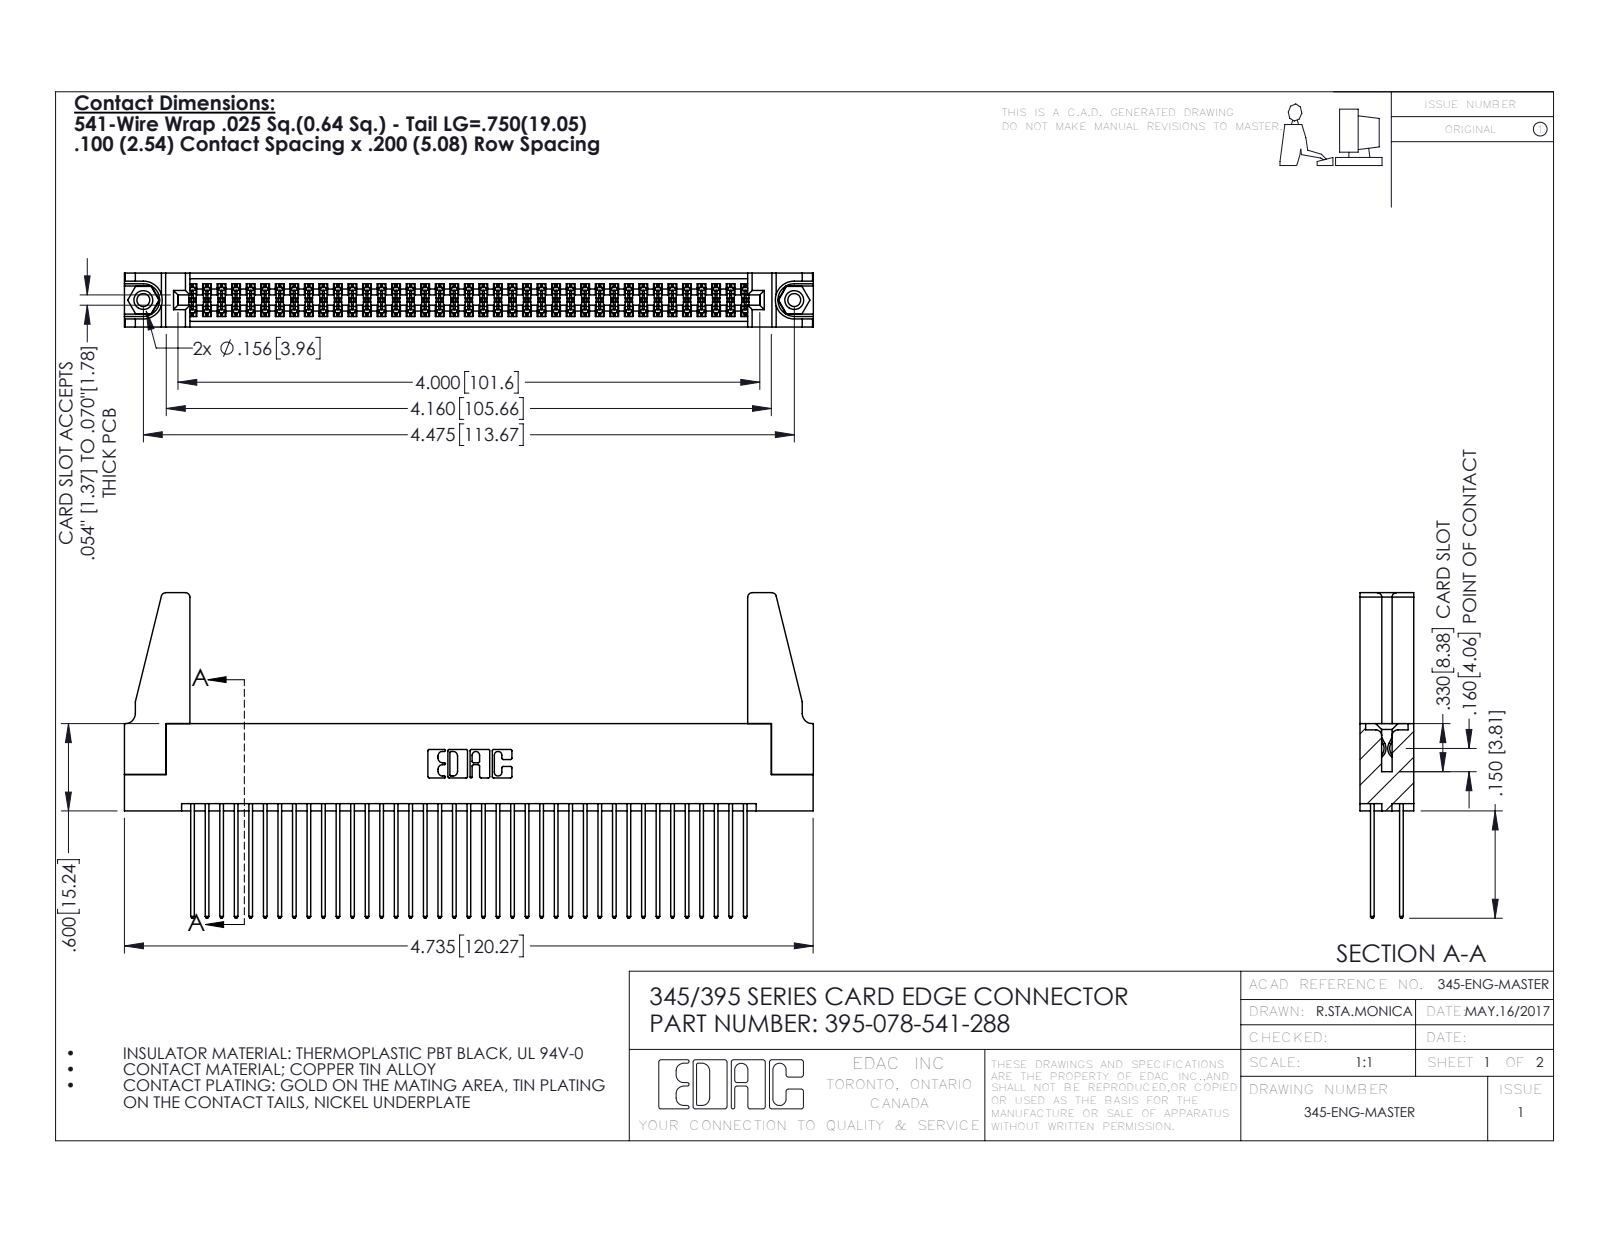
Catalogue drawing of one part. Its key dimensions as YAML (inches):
part_name: "345-220-078_345-220-088; 395-078-541-288; 345 Part_Flush Mounting Lugs - 0.156 Dia-TH; 345-250-001_345-250-001-102 (+1 more)"
step_written_by: "SolidWorks 2016 (CONFIG_CONTROL_DESIGN)"
units: inches
bodies: {solids: 83, faces: 4150, planar: 2726, cylindrical: 1408, other: 16}
overall_size: [4.736, 2.237, 0.37]
volume: 0.937
surface_area: 35.74
round_holes:
  - {diameter: 0.089, count: 2}
  - {diameter: 0.125, count: 2}
  - {diameter: 0.156, count: 2}
  - {diameter: 0.064, count: 1}
round_bosses_or_shafts:
  - {diameter: 0.155, count: 2}
partial_cylinders:
  - {radius: 0.006, count: 117}
  - {radius: 0.01, count: 78}
  - {radius: 0.01, count: 22}
  - {radius: 0.03, count: 8}
  - {radius: 0.007, count: 6}
  - {radius: 0.031, count: 6}
  - {radius: 0.026, count: 3}
  - {radius: 0.014, count: 2}
face_to_face_distances: [0.072, 0.298, 0.2, 0.098, 0.272, 0.025, 0.37, 0.225, 0.175, 0.149]
hole_center_spacings: [0.27, 4.239, 4.475]
